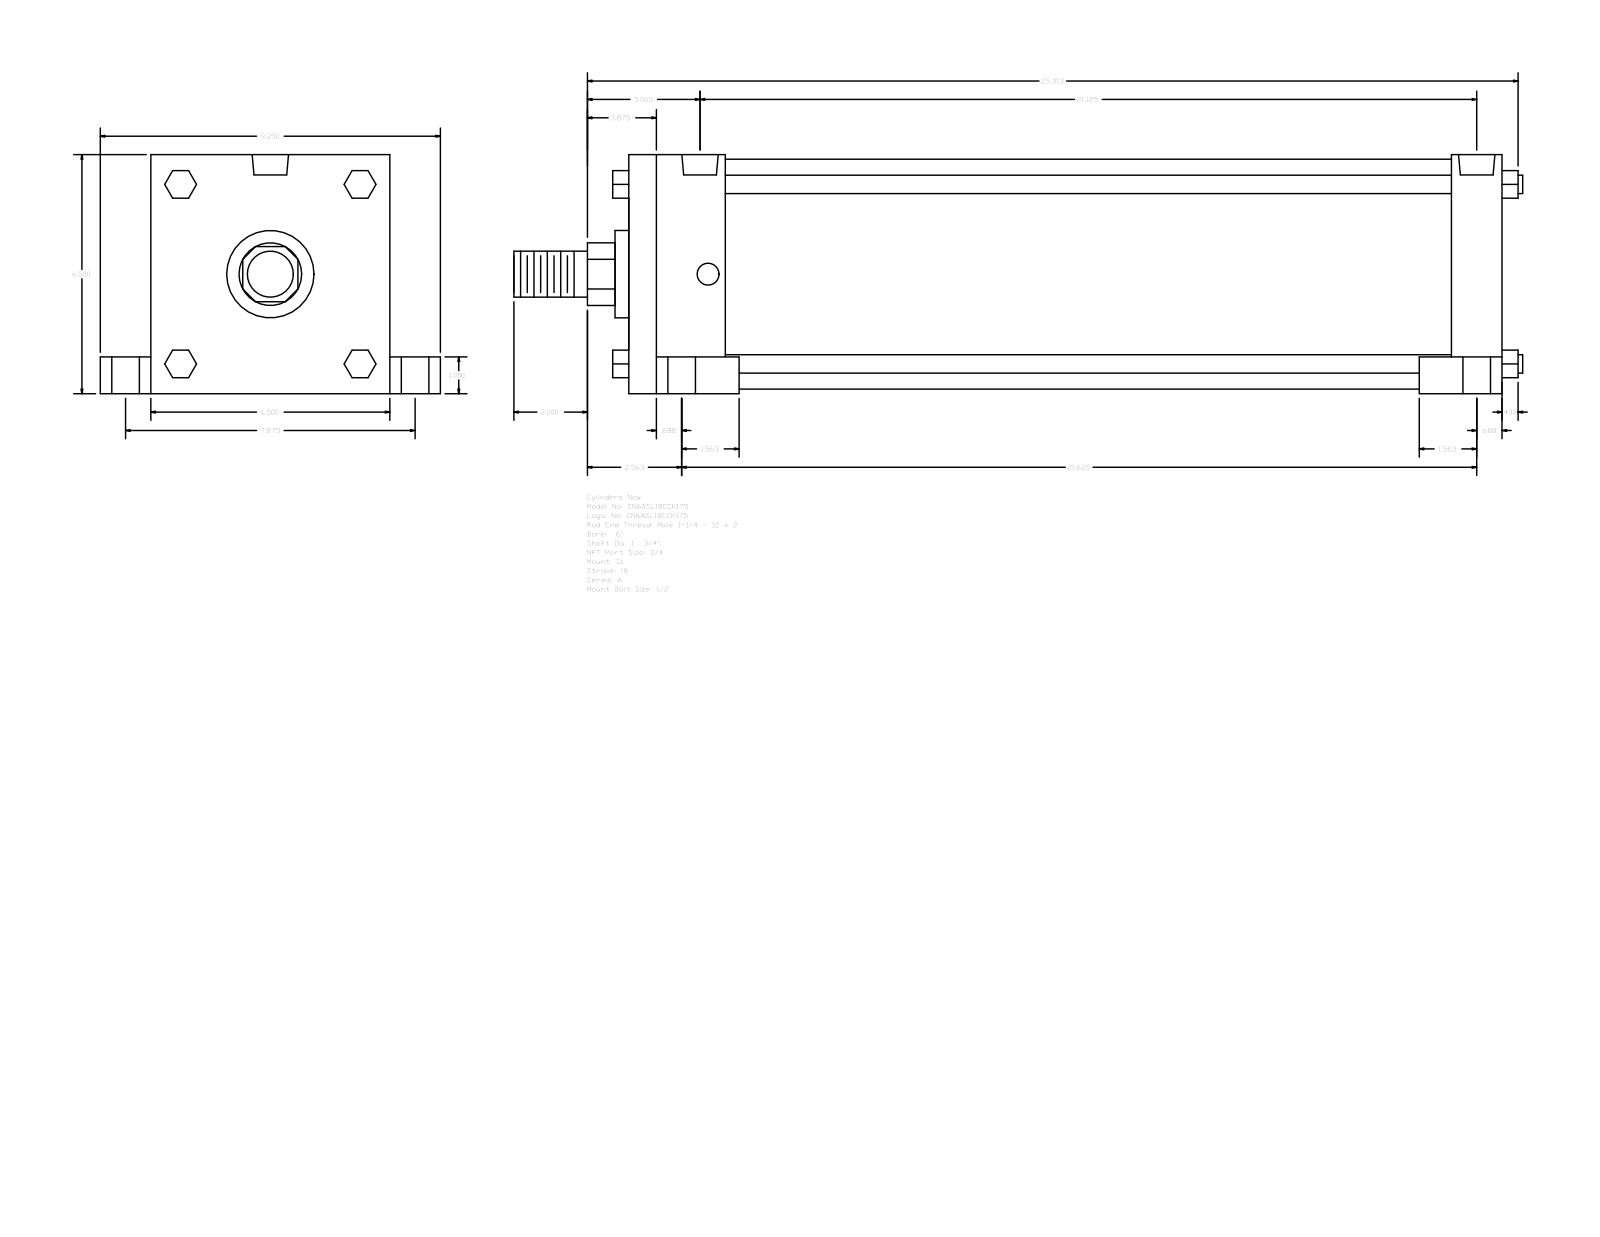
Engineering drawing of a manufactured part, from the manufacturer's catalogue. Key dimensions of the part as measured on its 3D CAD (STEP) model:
Part name (STEP PRODUCT): A_SL__0600_1.75
STEP written by: GSSL Pune (CONFIG_CONTROL_DESIGN)
Units: millimetres
Bodies: 0 solids, 150 faces (114 planar, 36 cylindrical, 0 other)
Overall size (bounding box): 696.91 × 234.95 × 165.1
Round holes (diameter × count): ⌀15.08 ×4, ⌀19.05 ×4, ⌀25.4 ×4, ⌀25.12 ×2
Round bosses / shafts (diameter × count): ⌀12.7 ×4, ⌀158.75 ×1, ⌀60.33 ×1, ⌀44.45 ×1, ⌀31.75 ×1
Partial cylindrical surfaces — rounded edges, fillets, slot ends (radius × count): R21.63 ×1
Main face-to-face distances: 165.1, 603.26, 66.68, 536.58, 568.33, 501.65, 34.93, 25.4, 139.7, 34.92
Hole centre spacings: 5.56, 100.01, 100.16, 100.81, 101.66, 200.02, 525.45, 531.01
